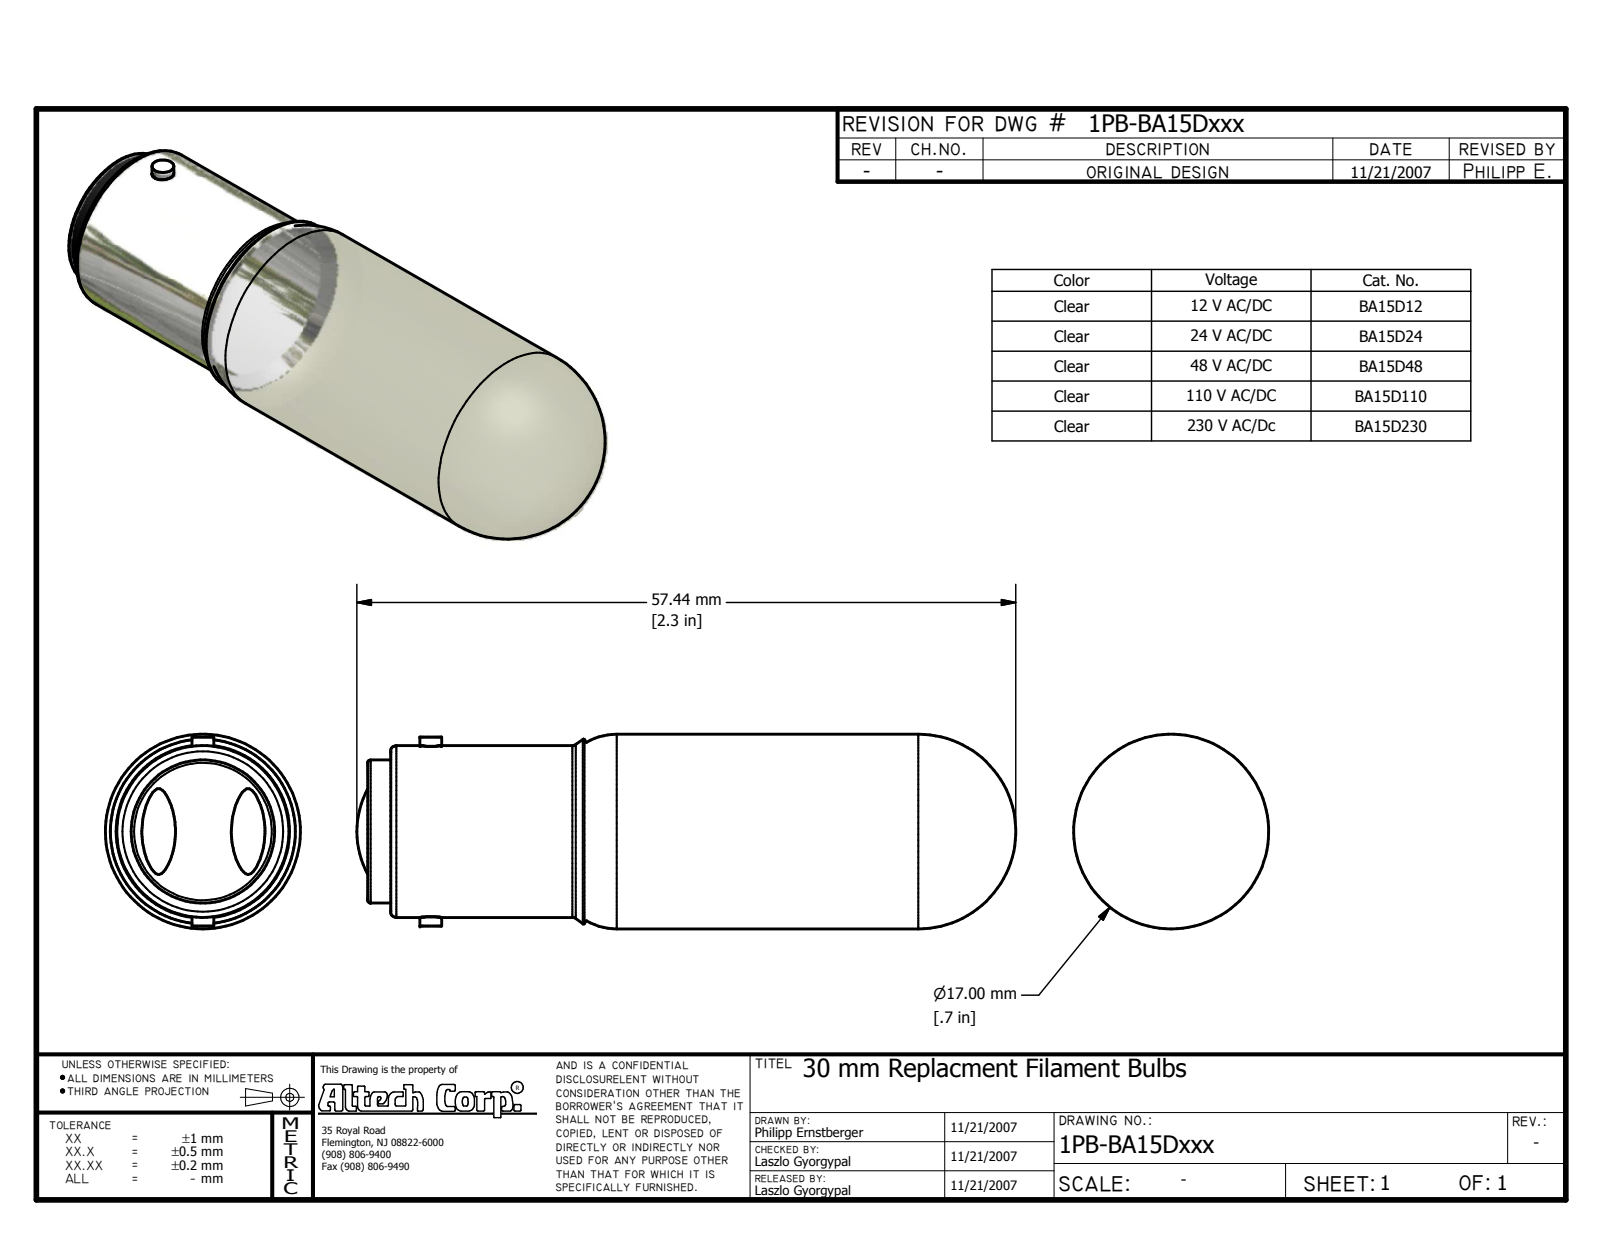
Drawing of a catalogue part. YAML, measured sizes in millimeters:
part_name: "BA15Dxxx; bulb"
step_written_by: "Autodesk Inventor 2008 (AUTOMOTIVE_DESIGN)"
units: millimeters
bodies: {solids: 2, faces: 36, planar: 11, cylindrical: 9, other: 16}
overall_size: [57.44, 17, 17]
volume: 900
surface_area: 6151
round_holes:
  - {diameter: 0.9, count: 1}
  - {diameter: 14, count: 1}
  - {diameter: 16.8, count: 1}
round_bosses_or_shafts:
  - {diameter: 17, count: 1}
  - {diameter: 15, count: 1}
  - {diameter: 12.5, count: 1}
  - {diameter: 1.9, count: 1}
face_to_face_distances: [2.5, 0.5, 2, 1.5, 16, 15.5, 17.5, 18, 16.5]
